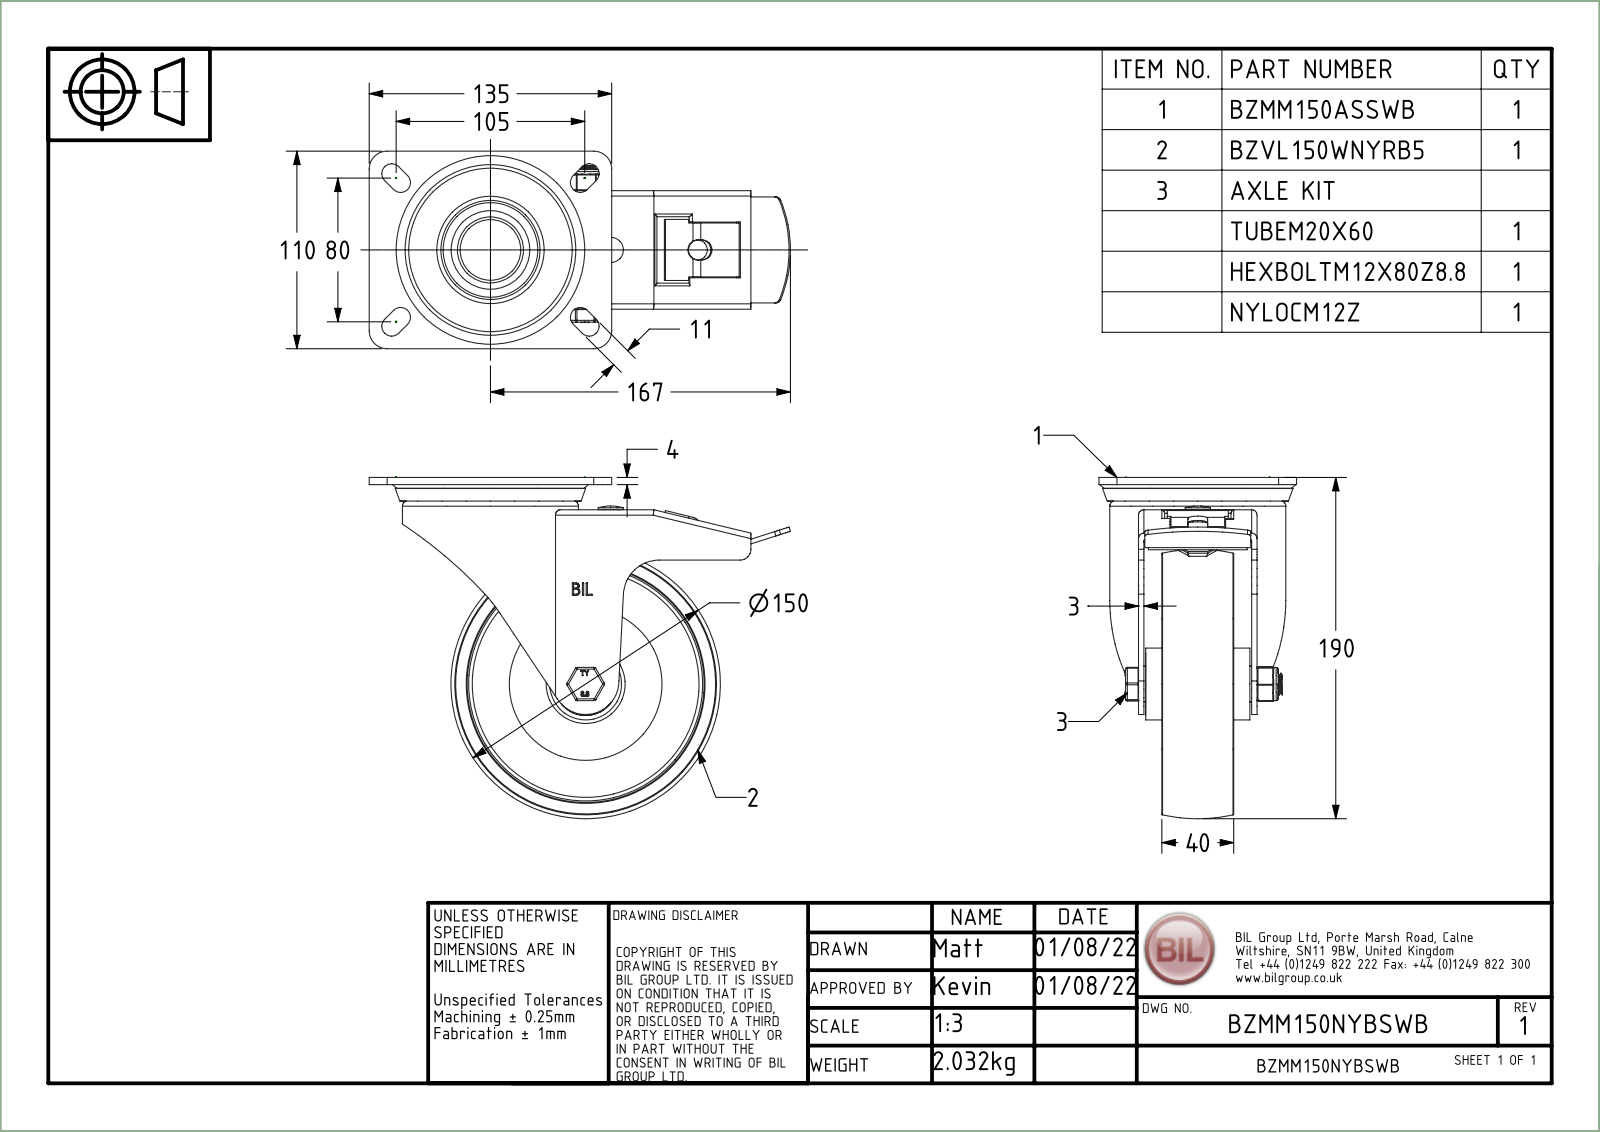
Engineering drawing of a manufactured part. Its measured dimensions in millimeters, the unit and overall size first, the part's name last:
Units: millimetres
Overall size (bounding box): 234.5 × 190 × 110
Round holes (diameter × count): ⌀8 ×1, ⌀11 ×1, ⌀12 ×1, ⌀12.2 ×1, ⌀12.5 ×1, ⌀14 ×1, ⌀20 ×1, ⌀20.2 ×1, ⌀33.75 ×1, ⌀35 ×1, ⌀39.75 ×1, ⌀92 ×1
Round bosses / shafts (diameter × count): ⌀7.5 ×8, ⌀98 ×1, ⌀78 ×1, ⌀50 ×1, ⌀40 ×1, ⌀34 ×1, ⌀19.9 ×1, ⌀18.5 ×1
Partial cylindrical surfaces — rounded edges, fillets, slot ends (radius × count): R0.5 ×18, R1 ×12, R1.5 ×10, R5.5 ×10, R0.25 ×6, R2.5 ×6, R3 ×6, R10 ×4
Main face-to-face distances: 3, 9, 5, 4, 8, 29, 16, 13, 26, 37
Hole centre spacings: 67
Volume: 538 388 mm³ · Surface area: 250 010 mm²
Bodies: 63 solids, 869 faces (309 planar, 321 cylindrical, 239 other)
Part name (STEP PRODUCT): ZINC PLATED, PRESSED STEEL TOP PLATE; ZINC PLATED, PRESSED STEEL TOP PLATE Geometry; BALL BEARINGS; BZMM150ASSWB (+7 more)
STEP written by: Spatial InterOp 3D (AUTOMOTIVE_DESIGN)
